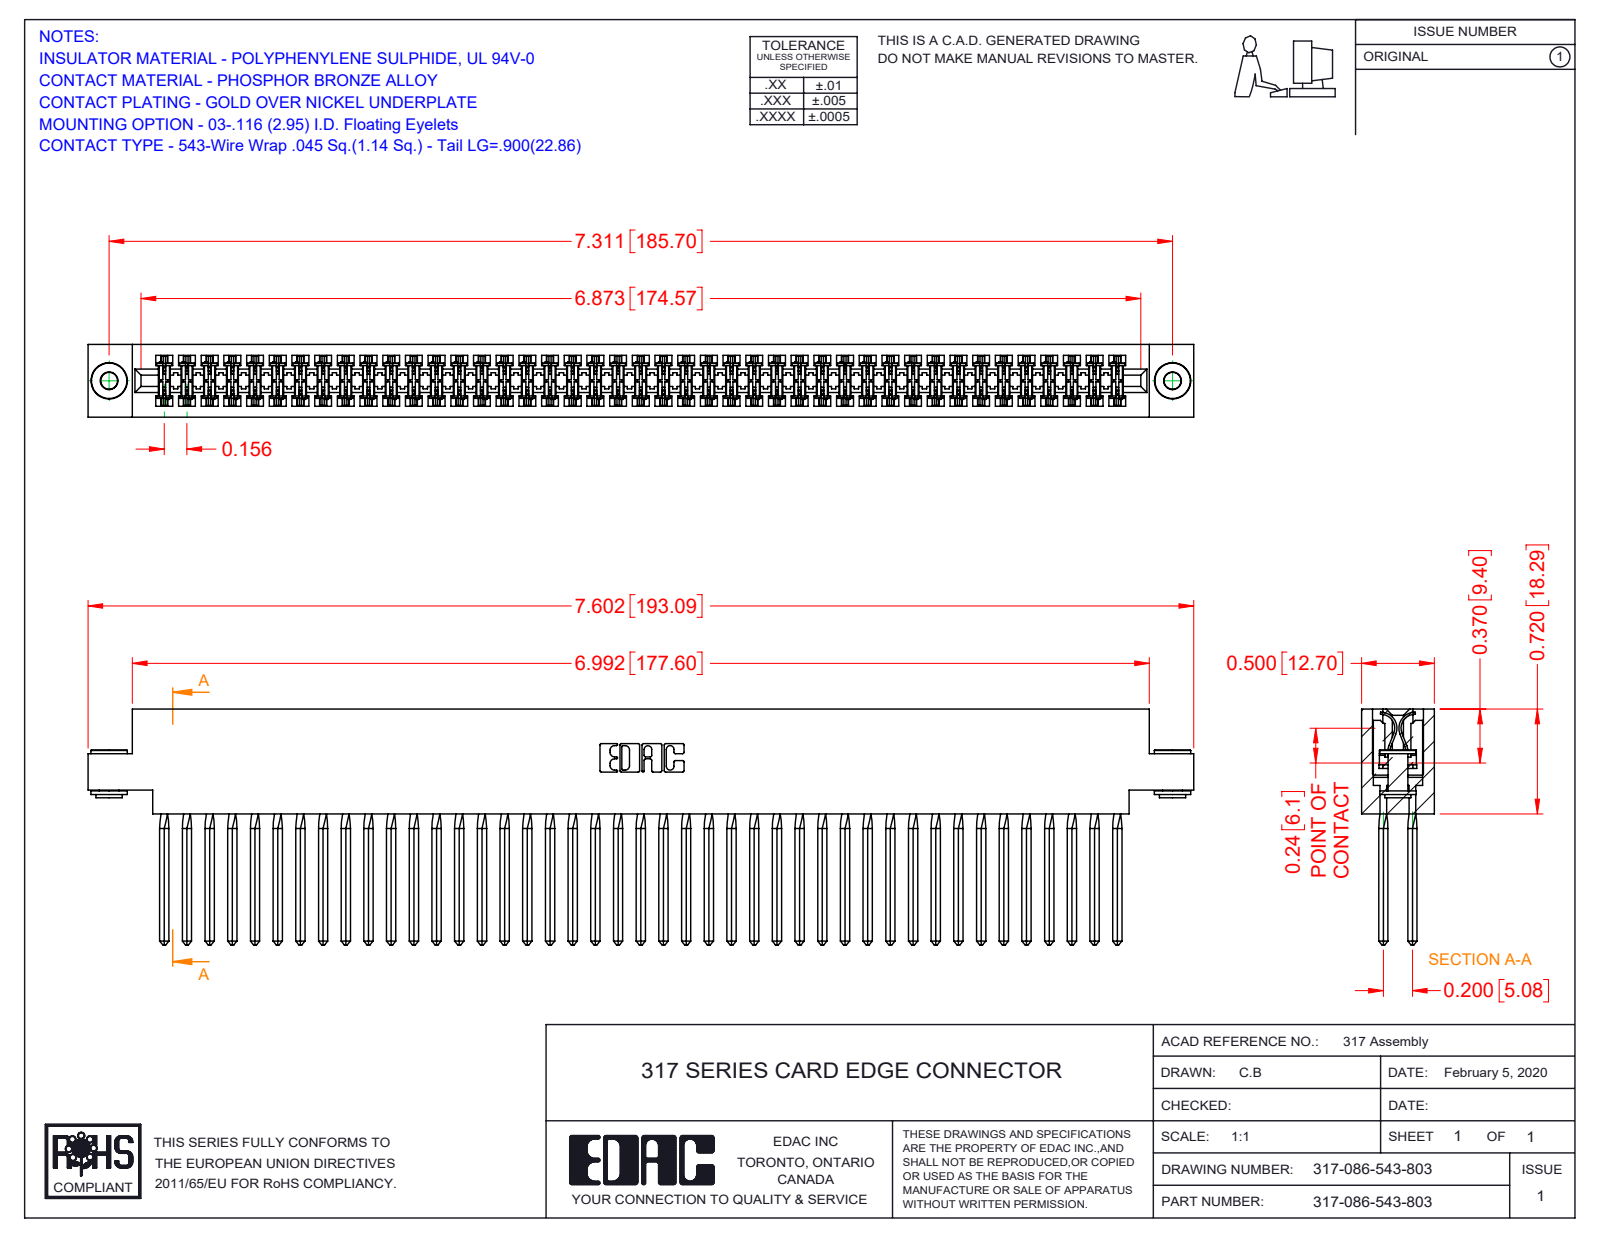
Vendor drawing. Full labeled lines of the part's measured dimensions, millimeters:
Part name (STEP PRODUCT): 345-250-002_345-250-002-102; 317-086-543-803; 317 Part_.156 Dia - TH; 317-290-001_543
STEP written by: SolidWorks 2016 (CONFIG_CONTROL_DESIGN)
Units: millimetres
Bodies: 89 solids, 7794 faces (6346 planar, 1096 cylindrical, 352 other)
Overall size (bounding box): 193.1 × 41.1 × 12.7
Volume: 32 890 mm³ · Surface area: 50 140 mm²
Round holes (diameter × count): ⌀2.9 ×2, ⌀4 ×2
Round bosses / shafts (diameter × count): ⌀6.4 ×2, ⌀4.6 ×2, ⌀3.5 ×2
Partial cylindrical surfaces — rounded edges, fillets, slot ends (radius × count): R0.4 ×172, R0.3 ×22, R0.2 ×6, R0.8 ×6, R0.7 ×3, R2.4 ×2, R2.5 ×2, R2.8 ×2
Main face-to-face distances: 12.7, 1.9, 10.8, 8.9, 5, 2.8, 2.4, 5.1, 2.9, 3.3
Hole centre spacings: 185.7
